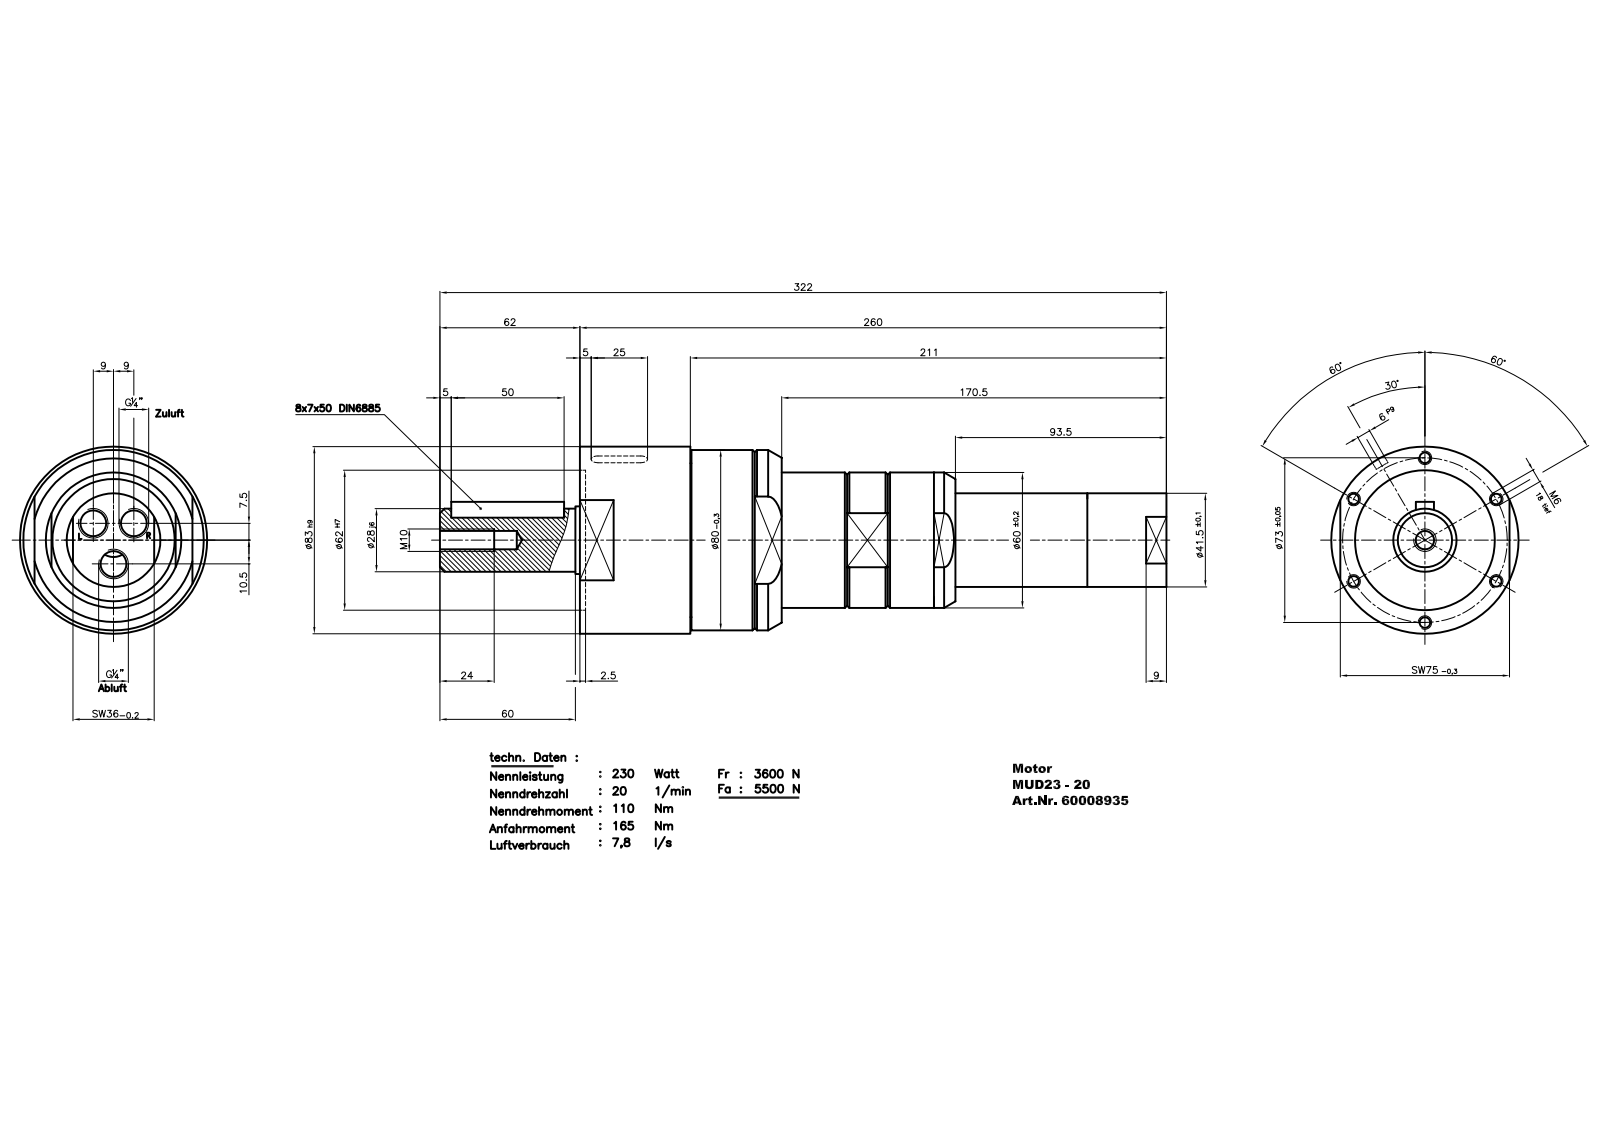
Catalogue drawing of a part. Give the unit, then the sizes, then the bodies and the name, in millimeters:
Units: millimetres
Overall size (bounding box): 322 × 83 × 83
Round holes (diameter × count): ⌀1.55 ×2, ⌀4 ×2, ⌀5.5 ×2, ⌀38 ×1, ⌀42 ×1, ⌀58.69 ×1, ⌀62 ×1
Round bosses / shafts (diameter × count): ⌀5 ×2, ⌀3.6 ×2, ⌀83 ×1, ⌀80 ×1, ⌀74.26 ×1, ⌀60 ×1, ⌀45 ×1, ⌀41.5 ×1
Partial cylindrical surfaces — rounded edges, fillets, slot ends (radius × count): R2.25 ×2, R3 ×2, R4 ×2, R32.5 ×2, R27.17 ×1
Main face-to-face distances: 3.64, 89.5, 85.86, 0.5, 77, 49, 45.36, 40.5, 260, 256.36
Volume: 820 732 mm³ · Surface area: 75 369 mm²
Bodies: 1 solid, 225 faces (121 planar, 43 cylindrical, 61 other)
Part name (STEP PRODUCT): MUD 23-20_60008935
STEP written by: Autodesk Inventor 2008 (AUTOMOTIVE_DESIGN)
